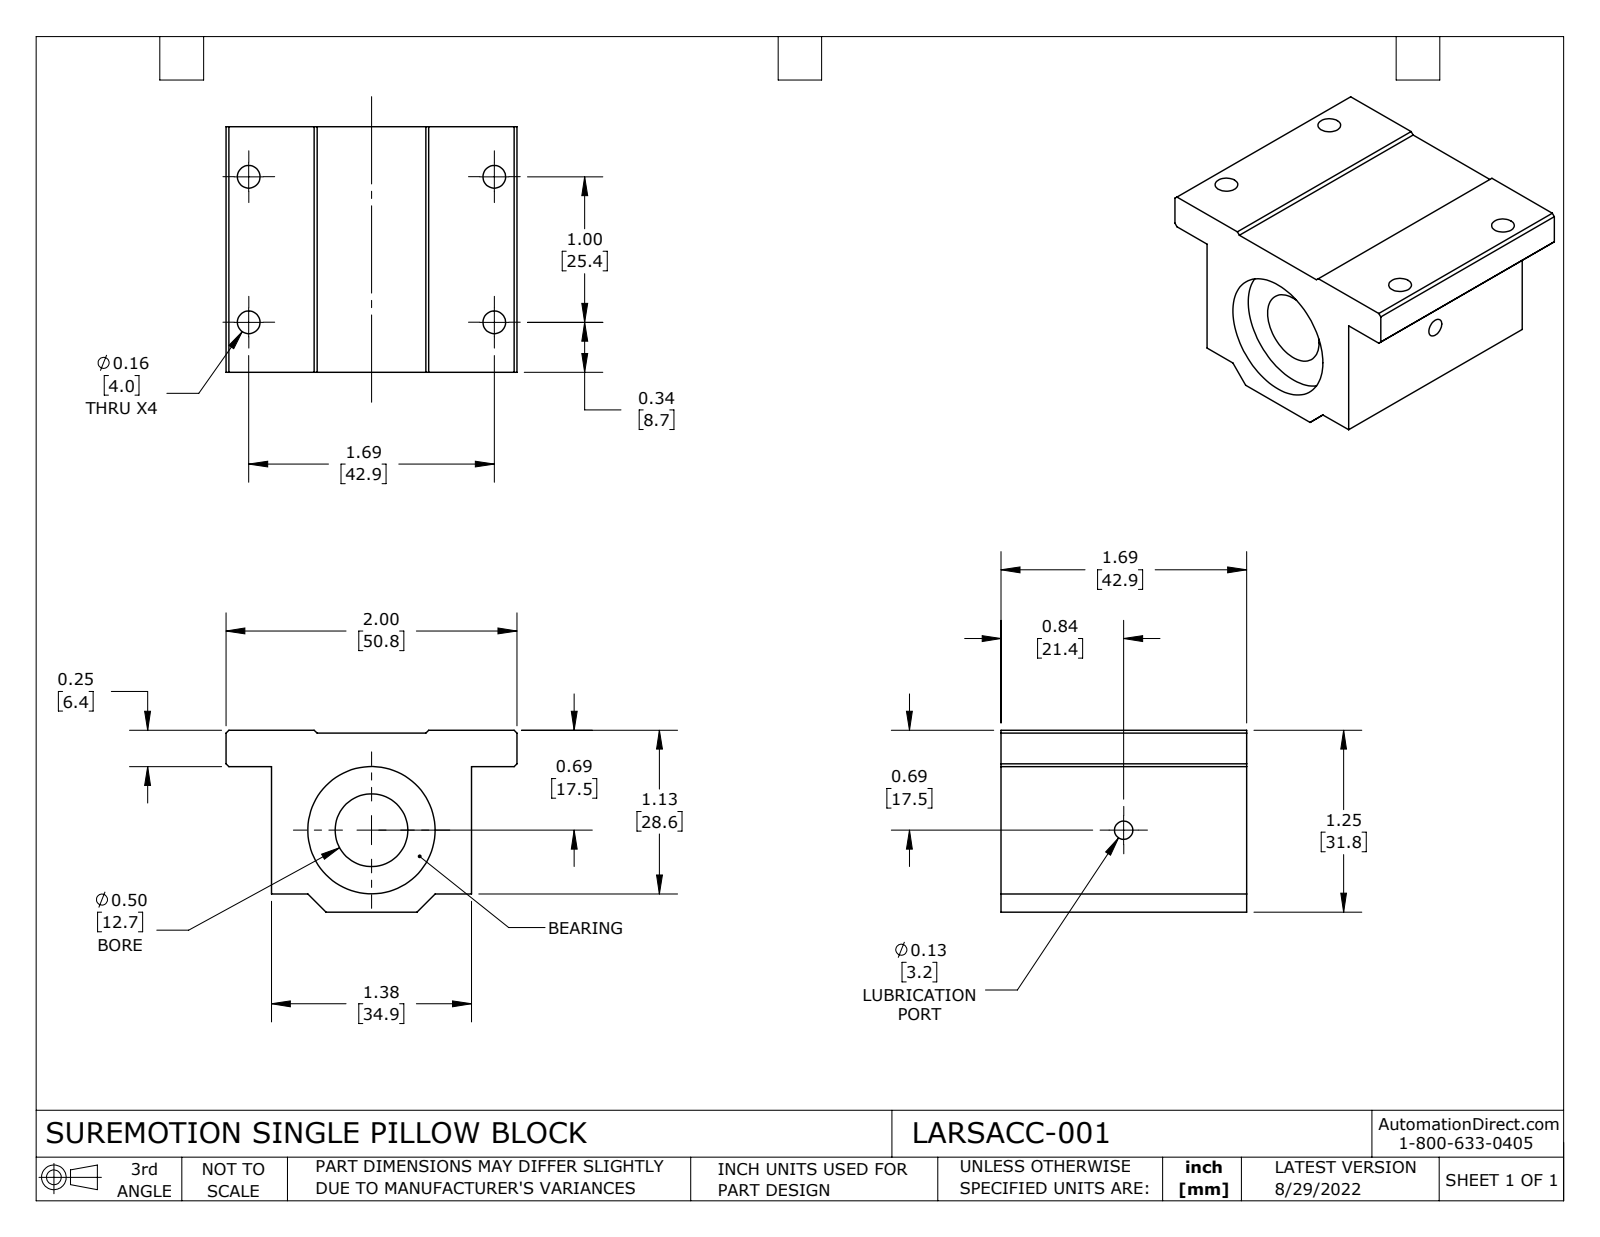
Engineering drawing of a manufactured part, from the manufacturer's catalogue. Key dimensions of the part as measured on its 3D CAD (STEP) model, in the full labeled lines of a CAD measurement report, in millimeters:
Part name (STEP PRODUCT): LARSACC-001
STEP written by: SolidWorks 2021 (CONFIG_CONTROL_DESIGN)
Units: millimetres
Bodies: 1 solid, 40 faces (24 planar, 16 cylindrical, 0 other)
Overall size (bounding box): 50.8 × 42.9 × 31.8
Volume: 41 440 mm³ · Surface area: 11 190 mm²
Round holes (diameter × count): ⌀4 ×4, ⌀3.2 ×1, ⌀12.7 ×1, ⌀22.2 ×1
Main face-to-face distances: 34.9, 0.5, 42.9, 31.2, 31.8, 25.4, 5.8, 6.4, 3.2, 22.2
Hole centre spacings: 25.4, 42.9, 49.8
